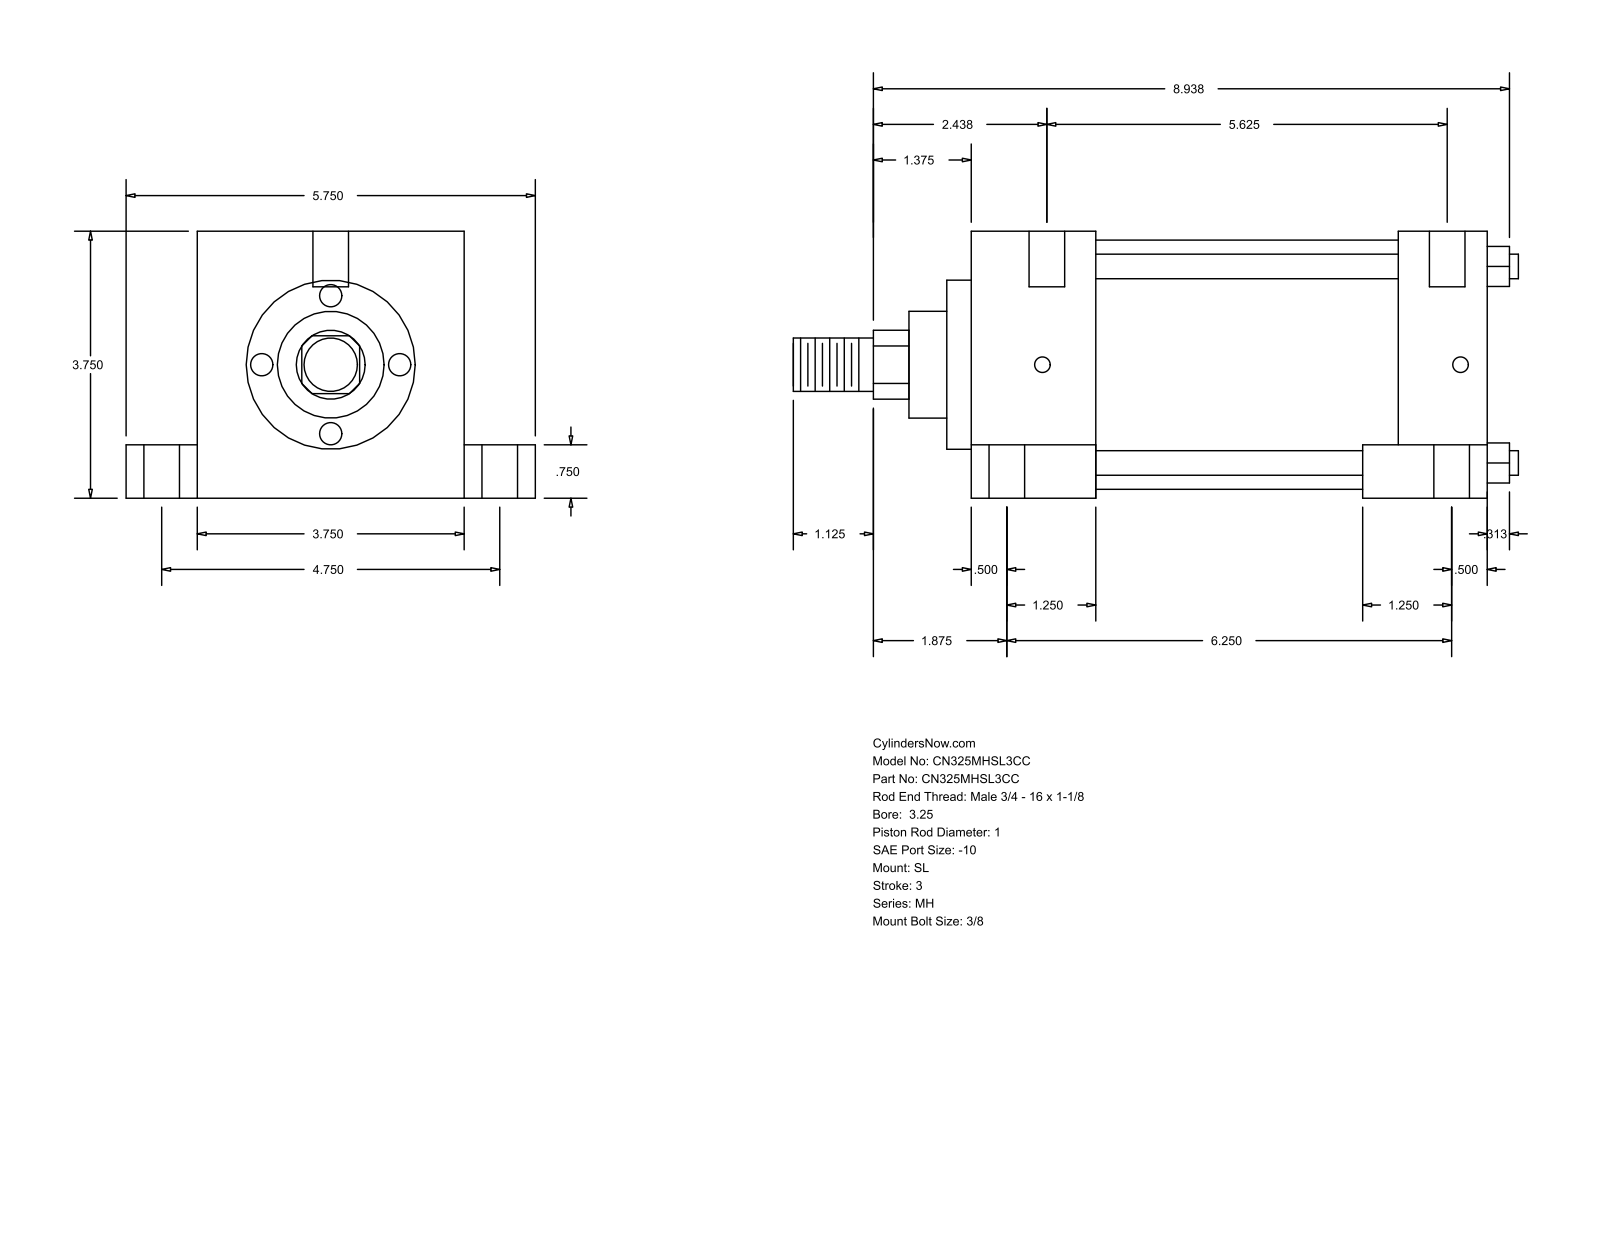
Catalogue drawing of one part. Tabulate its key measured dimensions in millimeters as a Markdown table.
| quantity | value |
| --- | --- |
| part name | MH_SL__0325_1 |
| STEP written by | GSSL Pune (CONFIG_CONTROL_DESIGN) |
| units | millimeters |
| bodies | 0 solids, 110 faces (77 planar, 33 cylindrical, 0 other) |
| overall size | 258.76 × 146.05 × 95.25 |
| round holes (diameter × count) | 12.7 × 6, 5.56 × 4, 19.05 × 4 |
| round bosses / shafts (diameter × count) | 8.76 × 4, 88.9 × 1, 60.33 × 1, 38.1 × 1, 25.4 × 1, 19.05 × 1 |
| partial cylindrical surfaces (radius × count) | 12.29 × 1 |
| main face-to-face distances | 95.24, 184.15, 44.46, 139.69, 25.41, 120.65, 19.05, 76.19, 152.4, 107.94 |
| hole center spacings | 60.35, 60.41, 61.65, 62, 120.66, 149.22, 156.56, 158.02 |
